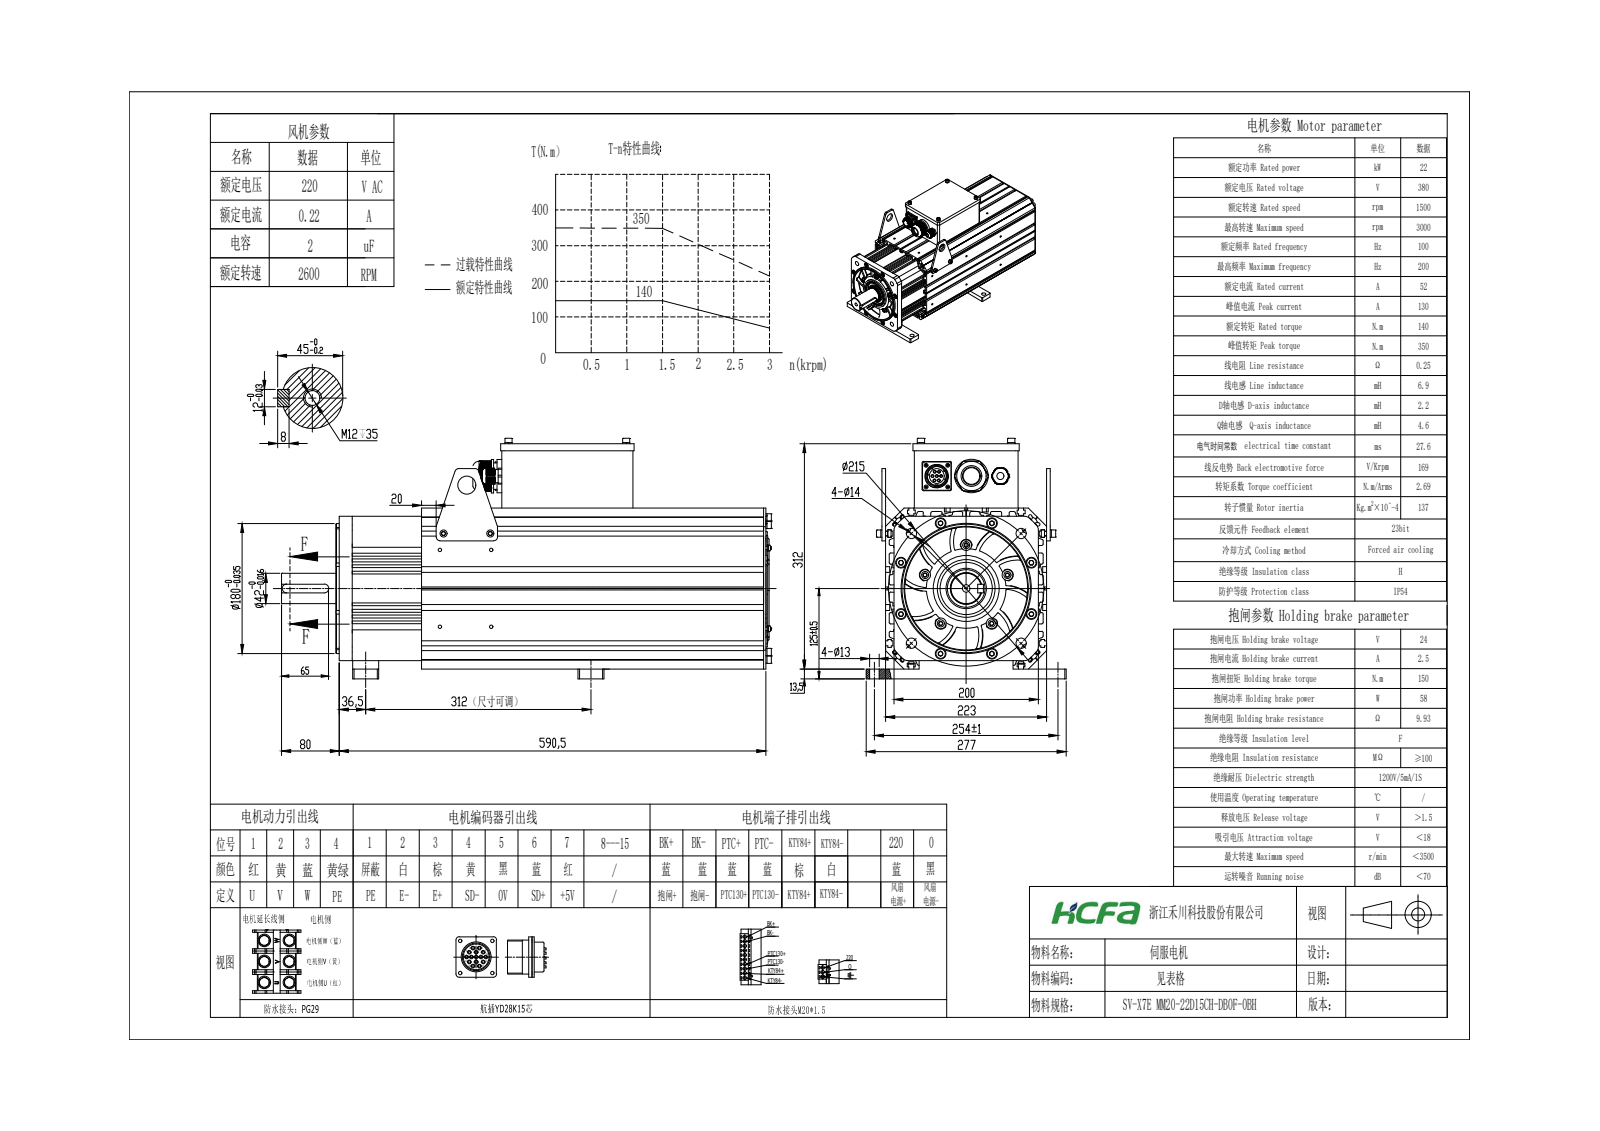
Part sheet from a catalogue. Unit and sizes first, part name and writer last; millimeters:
Units: millimetres
Overall size (bounding box): 678.1 × 333.1 × 277
Round holes (diameter × count): ⌀5 ×24, ⌀6.8 ×17, ⌀6.68 ×15, ⌀9 ×14, ⌀6.5 ×11, ⌀15 ×10, ⌀3.5 ×8, ⌀8 ×8, ⌀4.2 ×7, ⌀4.5 ×6, ⌀14 ×5, ⌀2.5 ×4
Round bosses / shafts (diameter × count): ⌀2 ×24, ⌀10 ×17, ⌀6 ×17, ⌀9.88 ×15, ⌀8 ×14, ⌀4 ×11, ⌀13 ×10, ⌀3 ×8
Partial cylindrical surfaces — rounded edges, fillets, slot ends (radius × count): R2 ×84, R0.5 ×24, R5 ×20, R3 ×15, R2.5 ×14, R10 ×12, R1.5 ×8, R2.41 ×8
Main face-to-face distances: 223, 2.5, 5, 218, 6.5, 11.5, 211.5, 206.5, 8, 198.5
Hole centre spacings: 148.5, 182.68, 106.4, 297, 72.86, 1.77, 41.18, 42.89
Volume: 7 580 000 mm³ · Surface area: 2 894 000 mm²
Bodies: 91 solids, 4316 faces (2345 planar, 1227 cylindrical, 744 other)
Part name (STEP PRODUCT): 22KW抱闸
STEP written by: SolidWorks 2021 (CONFIG_CONTROL_DESIGN)
